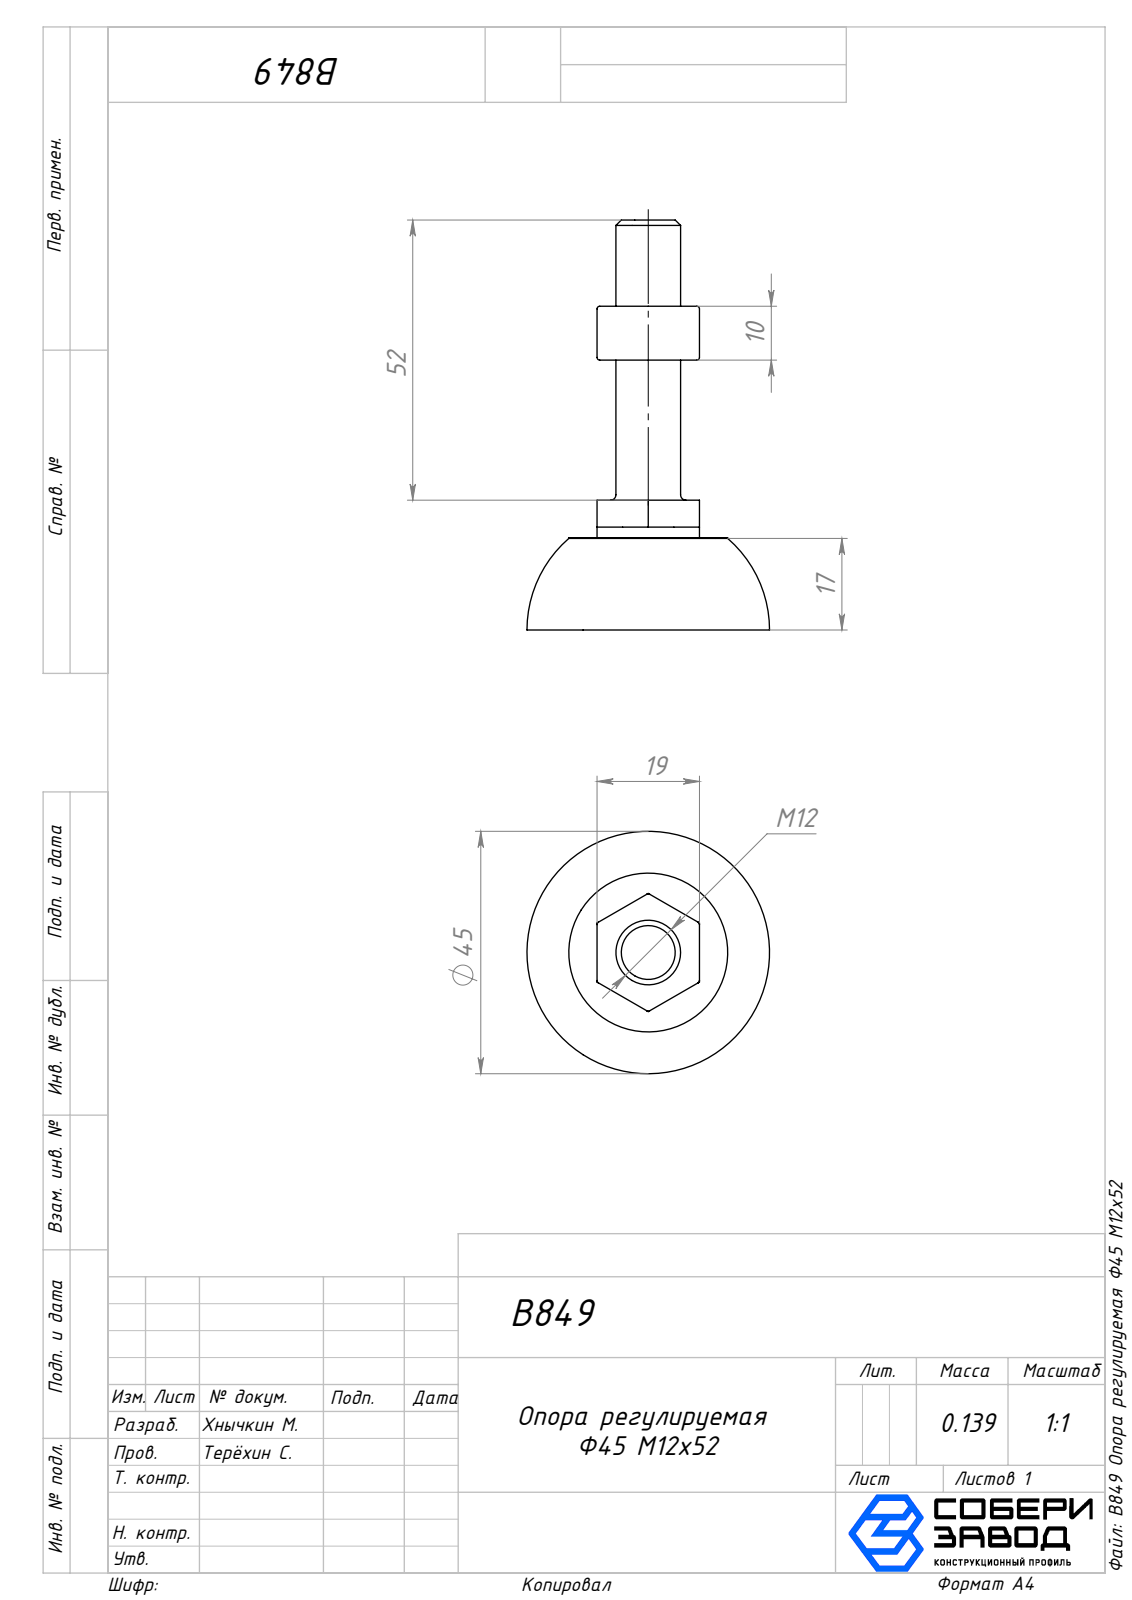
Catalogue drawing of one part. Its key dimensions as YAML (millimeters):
part_name: "Опора_00; B849 Опора регулируемая Ф45 М12х52; Вал_00; Мал. гайка_00 (+1 more)"
step_written_by: "SolidWorks 2025 (AUTOMOTIVE_DESIGN)"
units: millimeters
bodies: {solids: 4, faces: 125, planar: 35, cylindrical: 50, other: 40}
overall_size: [76.1, 45, 45]
volume: 19620
surface_area: 10547
round_holes:
  - {diameter: 4, count: 1}
  - {diameter: 5, count: 1}
  - {diameter: 10, count: 1}
round_bosses_or_shafts:
  - {diameter: 29.48, count: 1}
  - {diameter: 19, count: 1}
  - {diameter: 12, count: 1}
partial_cylinders:
  - {radius: 0.5, count: 36}
face_to_face_distances: [17.1, 19, 26, 10, 16.9, 43, 60.1, 43.2, 50.1, 33.2]
